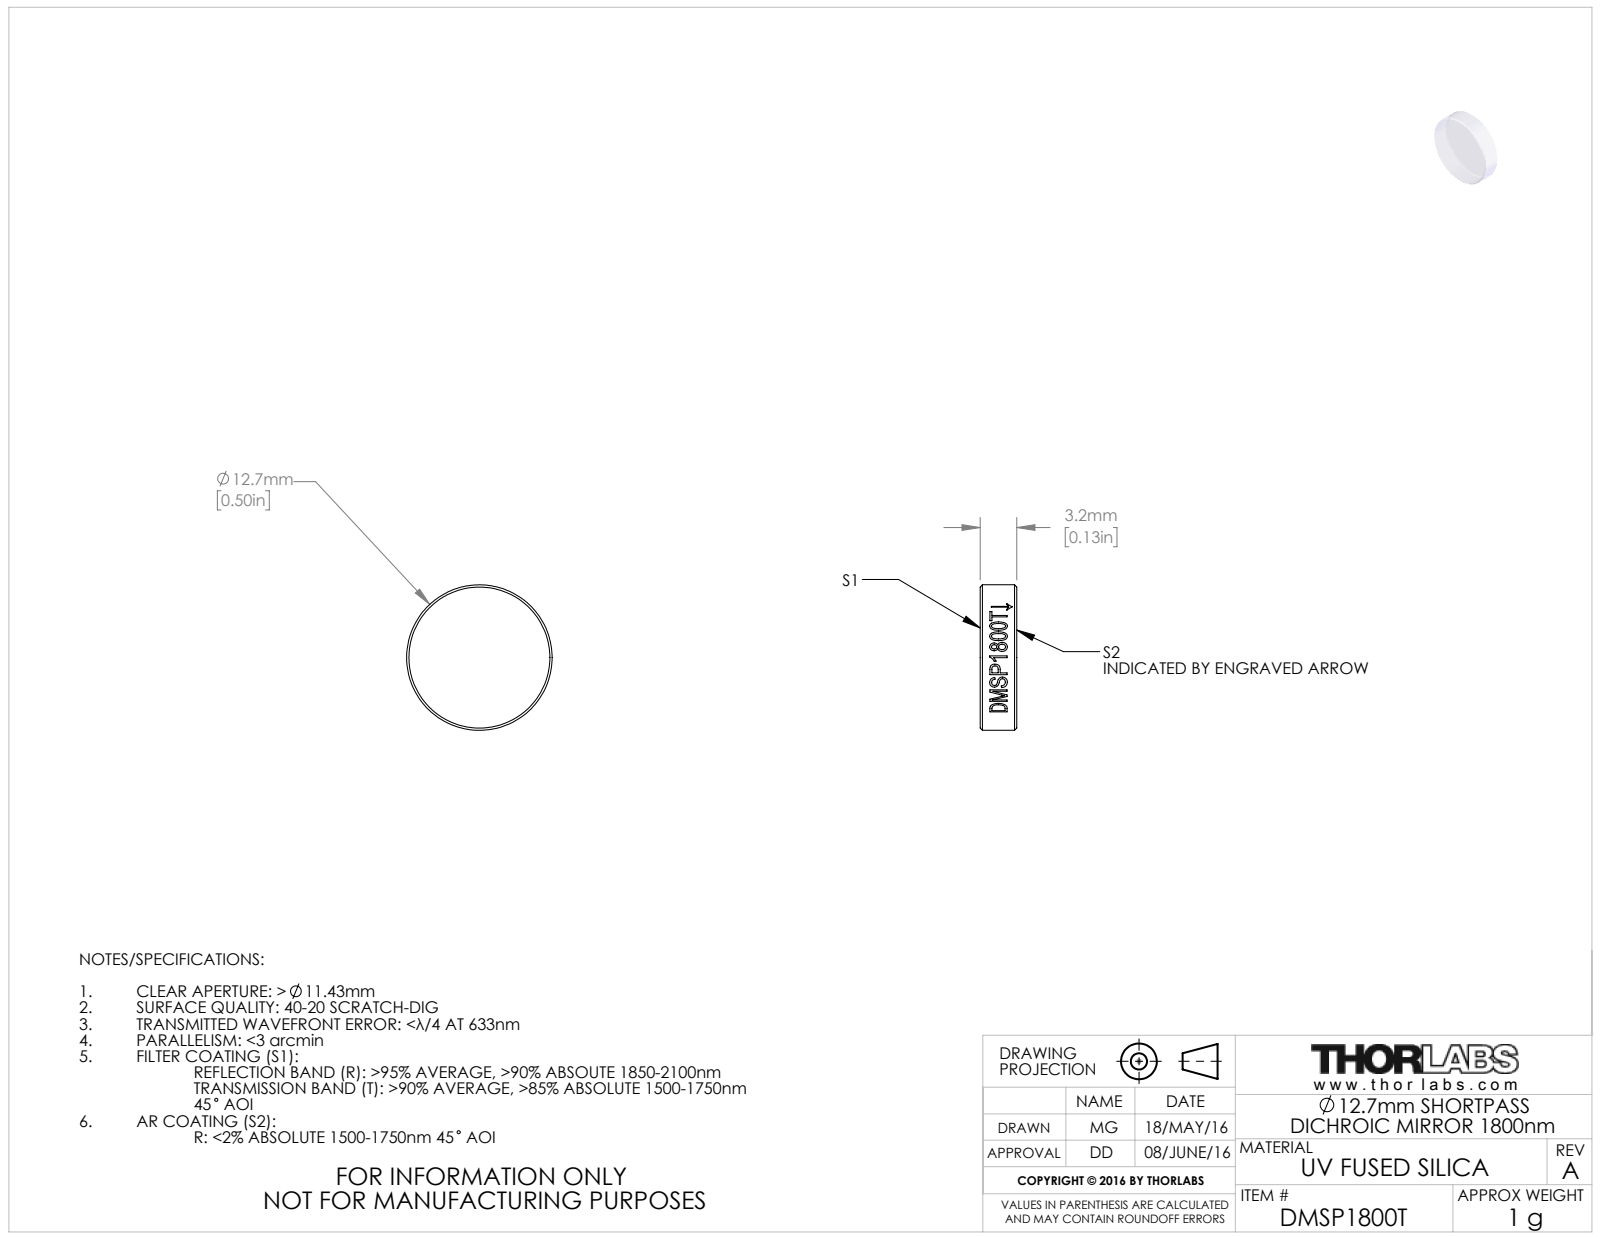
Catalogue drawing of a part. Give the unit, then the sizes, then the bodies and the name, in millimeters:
Units: millimetres
Overall size (bounding box): 12.7 × 12.7 × 3.2
Round bosses / shafts (diameter × count): ⌀12.7 ×1
Main face-to-face distances: 3.2
Volume: 404 mm³ · Surface area: 372 mm²
Bodies: 1 solid, 24 faces (2 planar, 18 cylindrical, 4 other)
Part name (STEP PRODUCT): TTN045301-E0W
STEP written by: SolidWorks 2016 (CONFIG_CONTROL_DESIGN)
